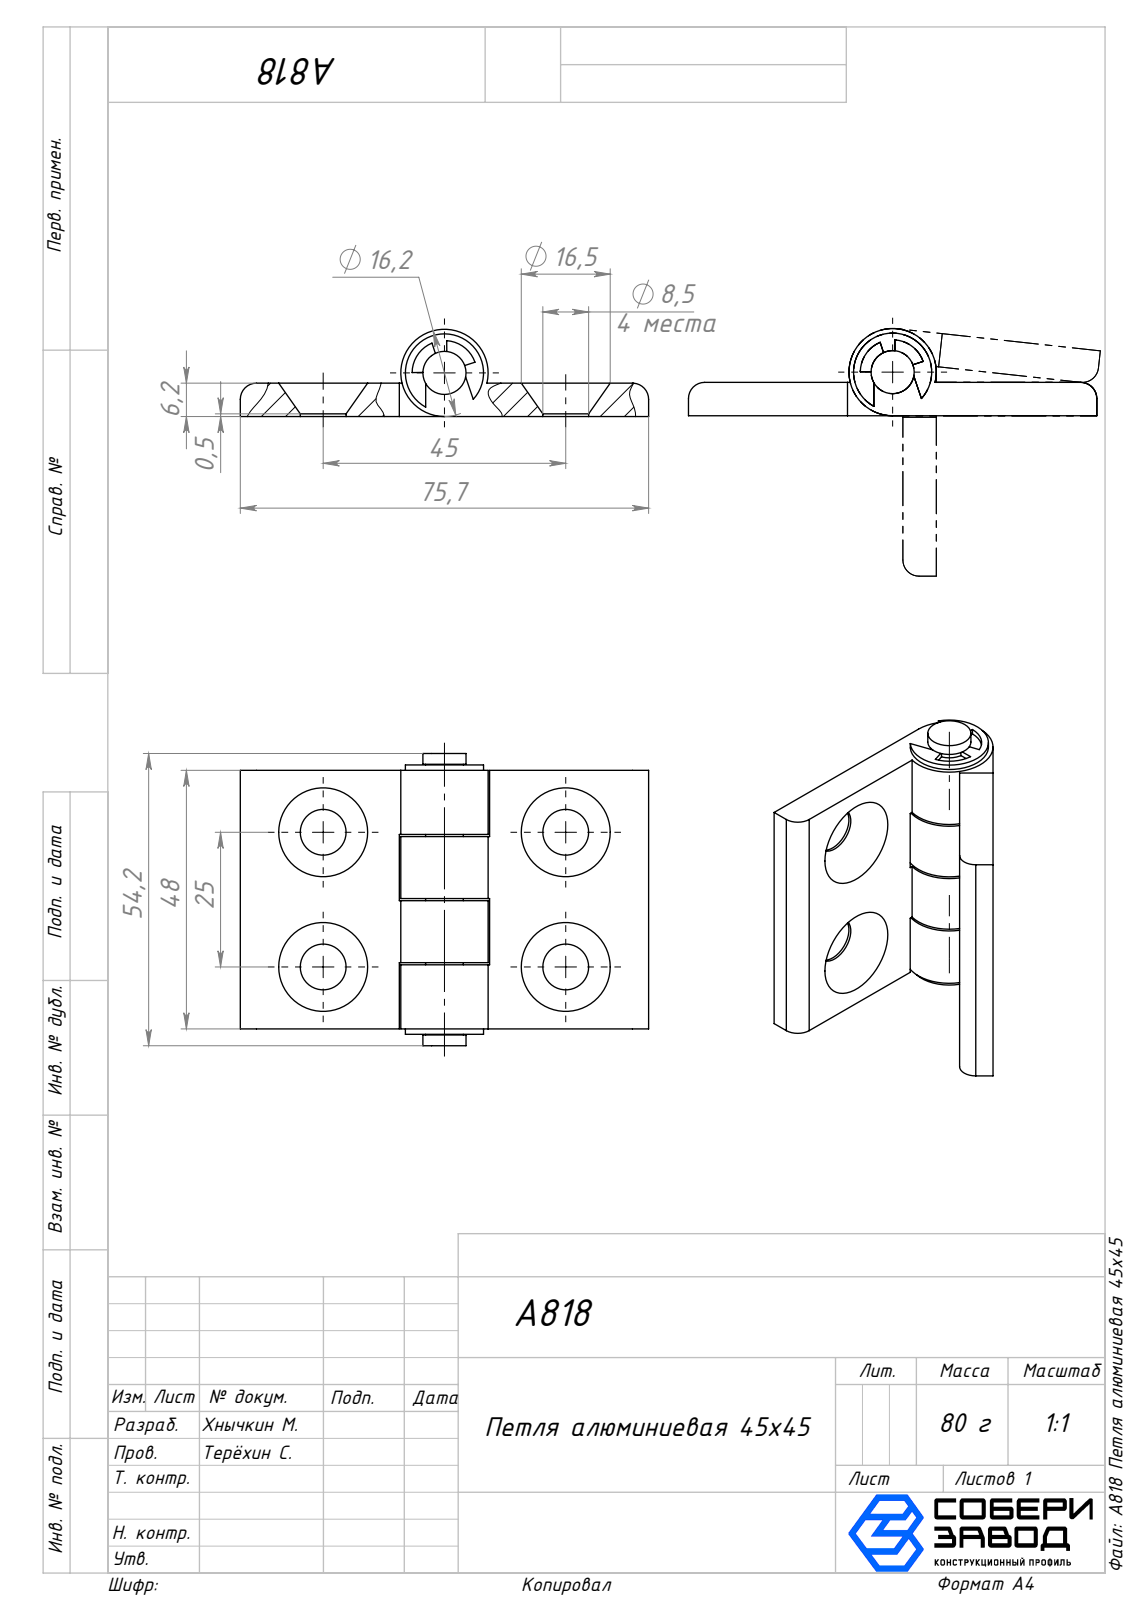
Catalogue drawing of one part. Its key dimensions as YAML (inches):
part_name: "A818 Петля алюминиевая 45х45; A818 Петля, часть 45 серии_00; A818 Палец_01; A818 Кольцо_00"
step_written_by: "SolidWorks 2025 (AUTOMOTIVE_DESIGN)"
units: inches
bodies: {solids: 5, faces: 98, planar: 40, cylindrical: 50, other: 8}
overall_size: [2.982, 2.136, 0.638]
volume: 1.538
surface_area: 21.31
round_holes:
  - {diameter: 0.335, count: 4}
  - {diameter: 0.276, count: 1}
round_bosses_or_shafts:
  - {diameter: 0.638, count: 1}
  - {diameter: 0.315, count: 1}
partial_cylinders:
  - {radius: 0.118, count: 2}
  - {radius: 0.236, count: 1}
  - {radius: 0.285, count: 1}
face_to_face_distances: [0.244, 0.469, 0.484, 0.937, 1.89, 0.953, 0.016, 1.406, 1.421, 0.453]
hole_center_spacings: [0.984, 1.772, 2.027]
